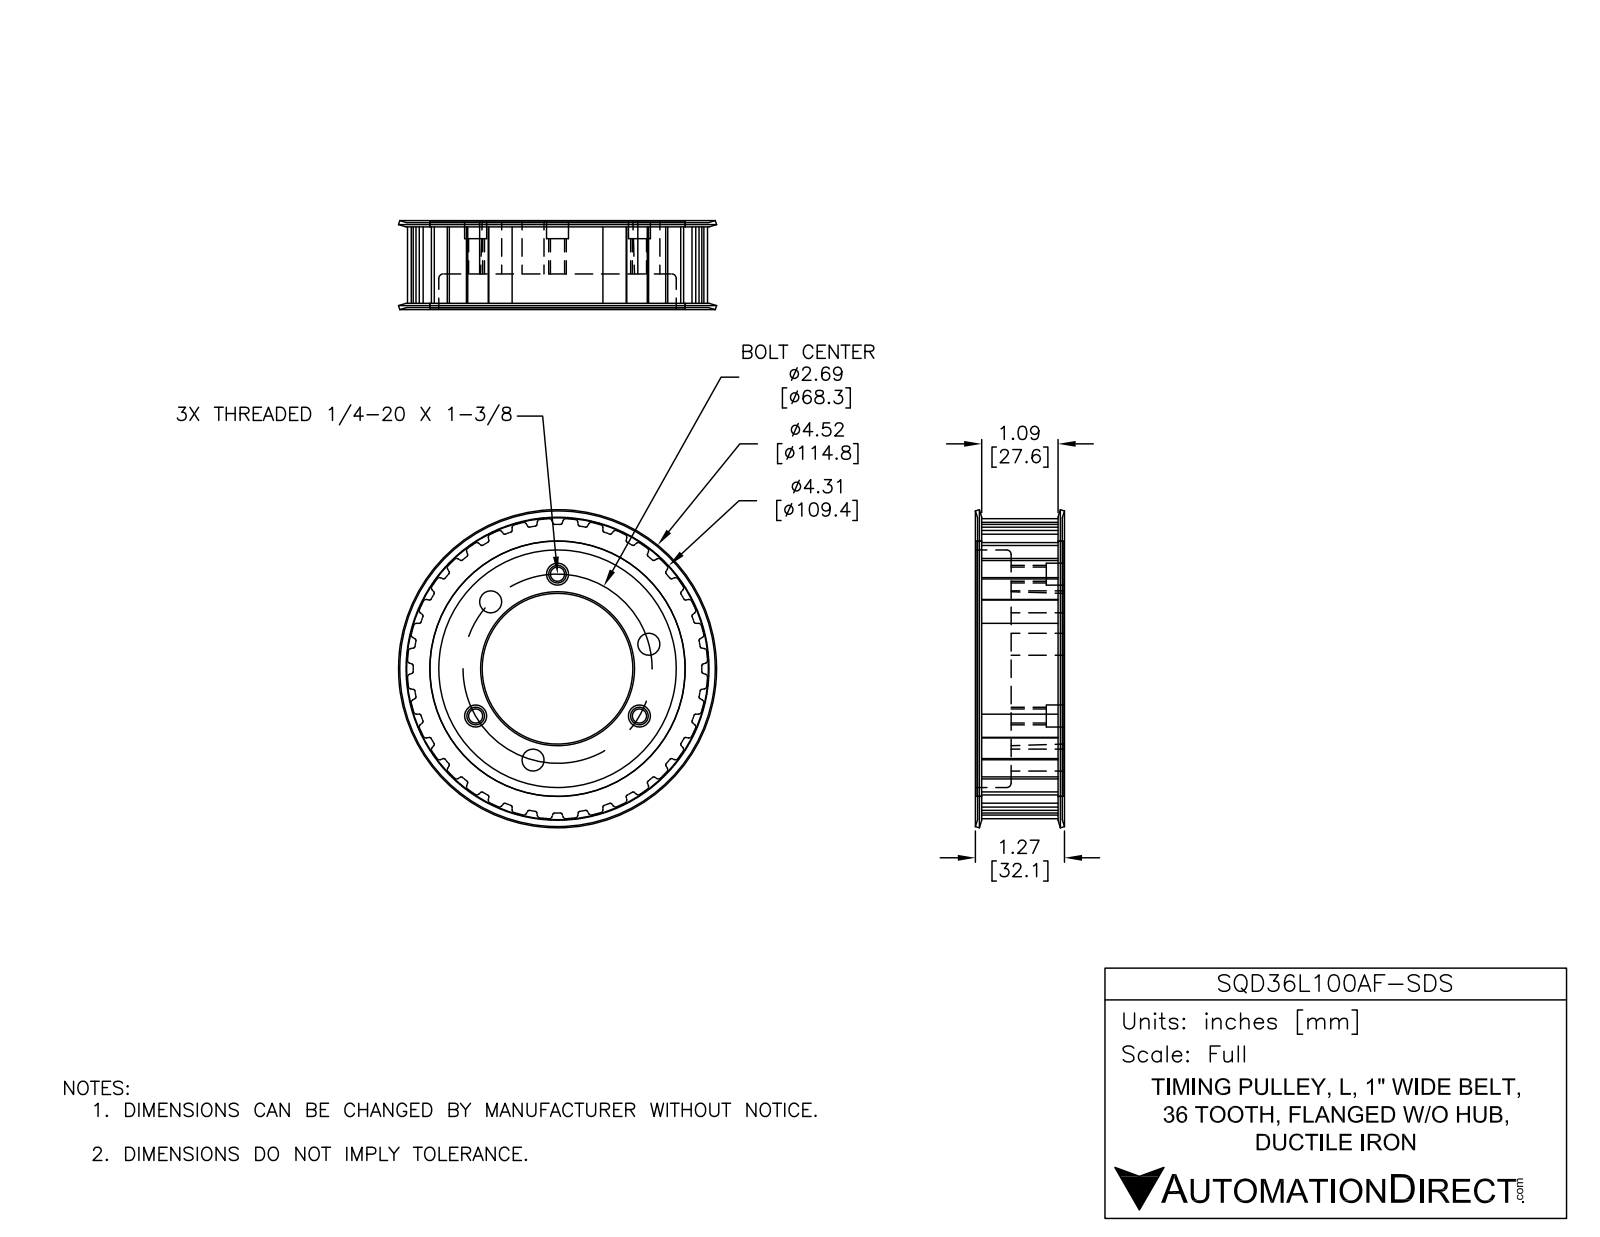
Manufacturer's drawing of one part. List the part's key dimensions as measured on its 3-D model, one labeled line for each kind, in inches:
Part name (STEP PRODUCT): SQD36L100AF-SDS
STEP written by: SolidWorks 2018 (AUTOMOTIVE_DESIGN)
Units: inches
Bodies: 4 solids, 370 faces (120 planar, 234 cylindrical, 16 other)
Overall size (bounding box): 4.52 × 4.52 × 1.265
Volume: 9.914 in³ · Surface area: 104.1 in²
Round holes (diameter × count): ⌀0.313 ×6, ⌀0.201 ×3, ⌀3.375 ×1, ⌀3.626 ×1, ⌀3.629 ×1
Partial cylindrical surfaces — rounded edges, fillets, slot ends (radius × count): R0.021 ×72, R0.04 ×72, R2.135 ×1
Main face-to-face distances: 0.06, 1.145, 1.085, 0.083, 1.168, 0.75, 0.667, 0.418, 0.023, 1.228
Hole centre spacings: 1.344, 2.327, 2.328, 2.665, 1.028, 1.636, 1.029, 1.343
